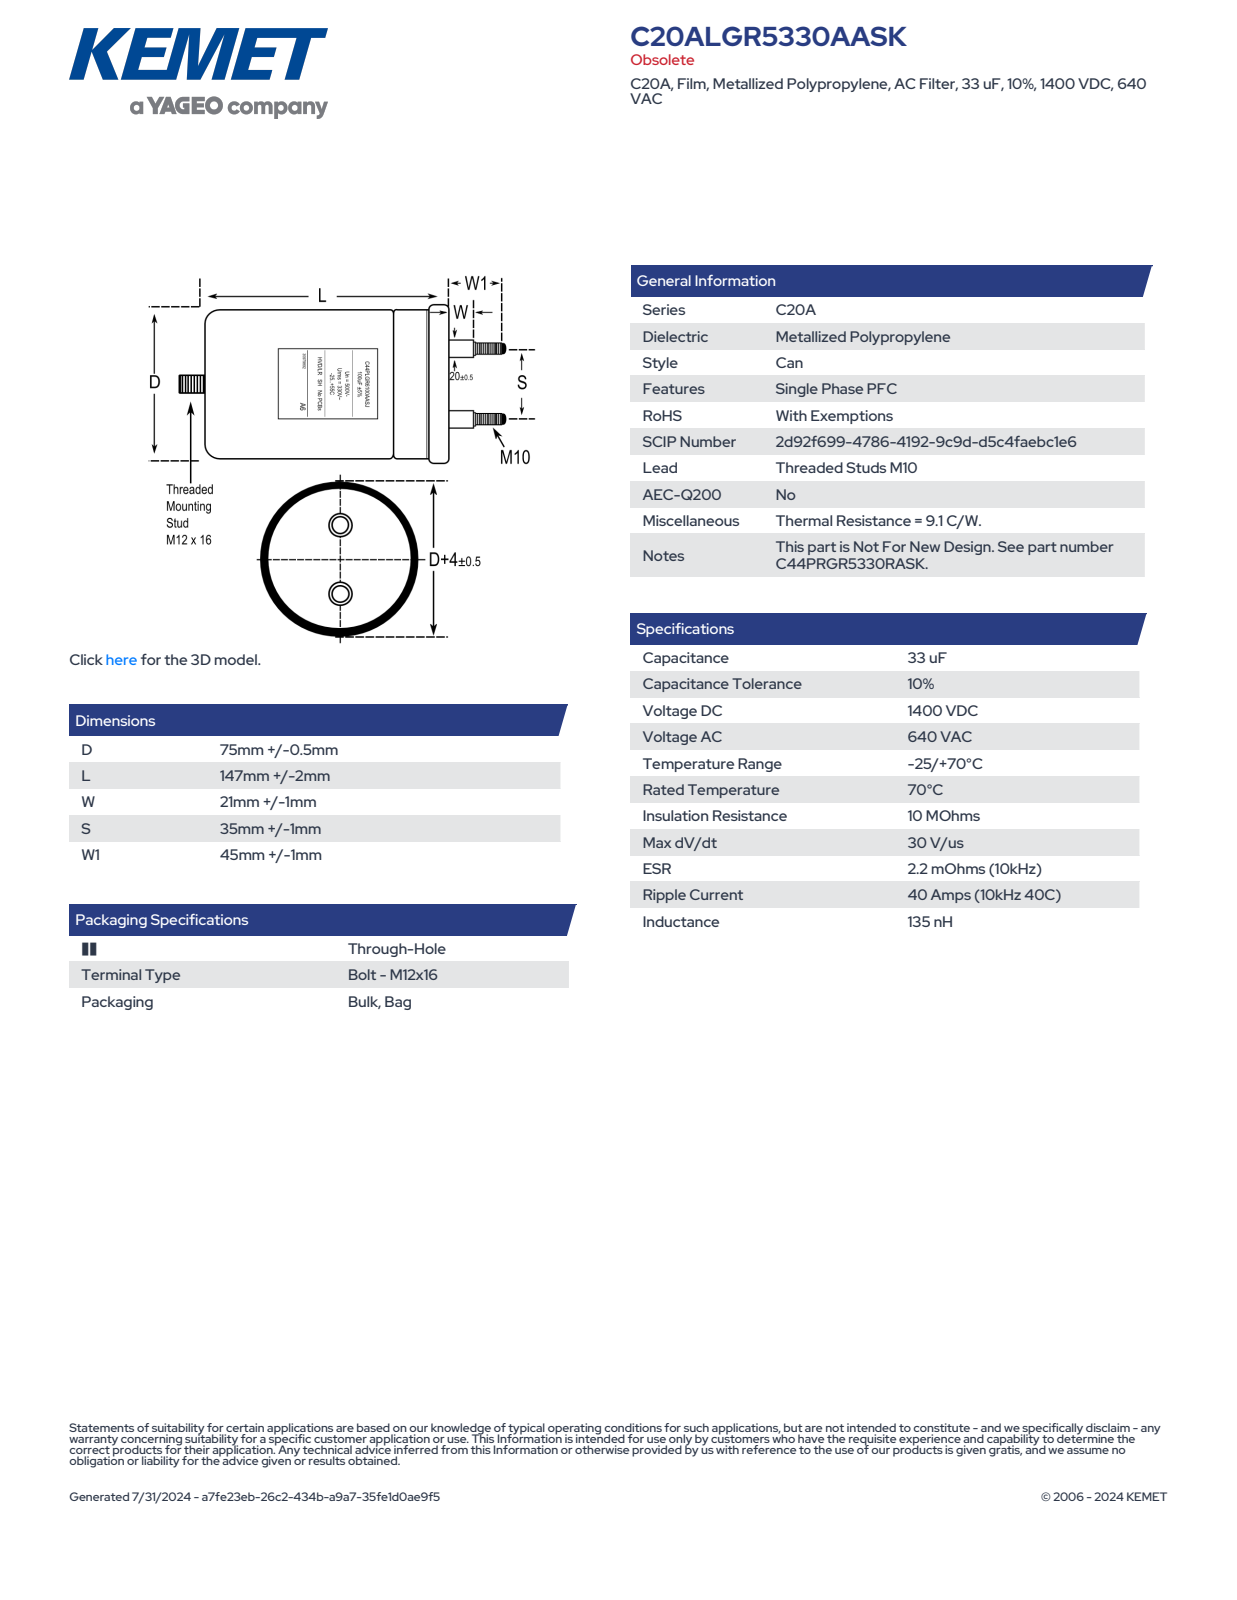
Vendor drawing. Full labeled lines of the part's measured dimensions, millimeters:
Part name (STEP PRODUCT): CFP_C44P_75X147_D75.5L149S35
STEP written by: SolidWorks 2014 (AUTOMOTIVE_DESIGN)
Units: millimetres
Bodies: 1 solid, 105 faces (32 planar, 36 cylindrical, 37 other)
Overall size (bounding box): 211 × 80 × 80
Volume: 688 026 mm³ · Surface area: 49 620 mm²
Round bosses / shafts (diameter × count): ⌀12 ×3, ⌀20.5 ×2, ⌀10 ×2, ⌀80 ×1, ⌀75.5 ×1
Partial cylindrical surfaces — rounded edges, fillets, slot ends (radius × count): R37.76 ×1
Main face-to-face distances: 149, 170, 21, 144.22, 4.78, 25.78, 195, 50.78, 46, 25
